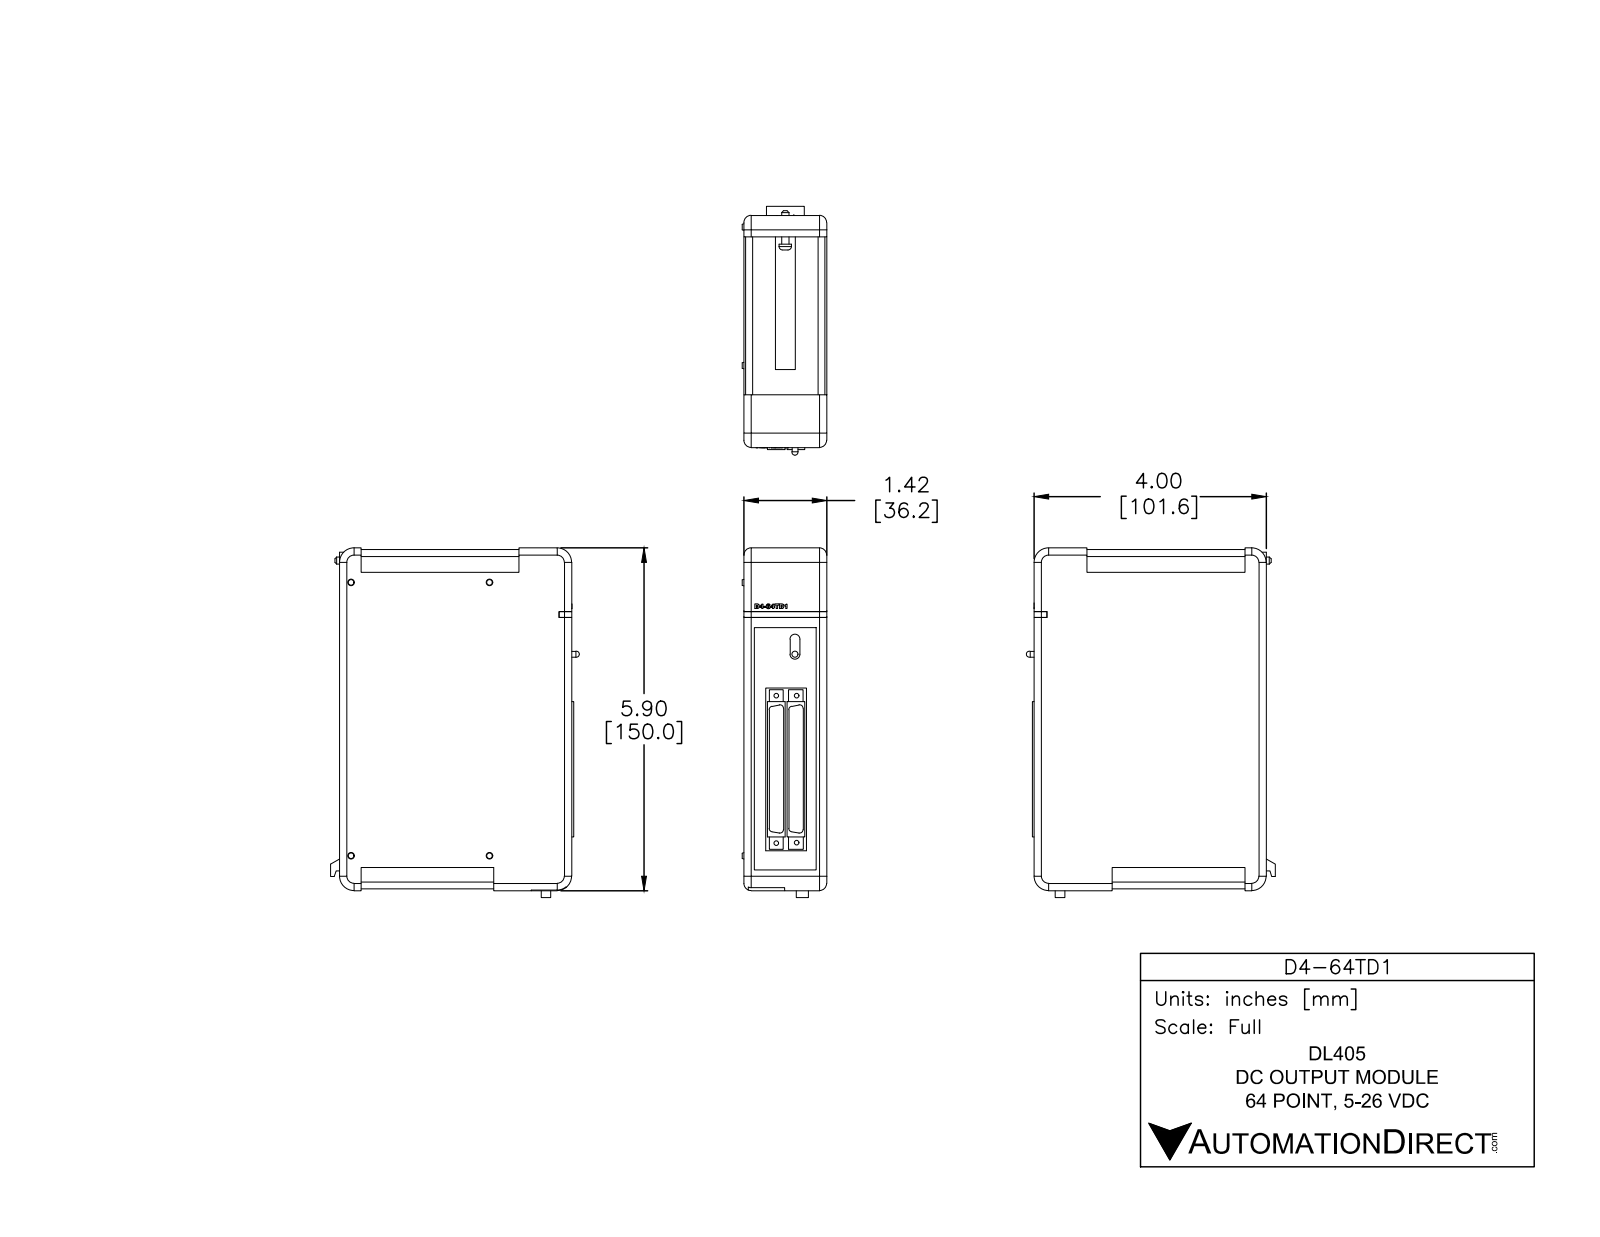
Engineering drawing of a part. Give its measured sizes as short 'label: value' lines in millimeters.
name: D4-64TD1
written by: SolidWorks 2014 (AUTOMOTIVE_DESIGN)
unit: mm
bodies: 2 solids, 313 faces (212 planar, 54 cylindrical, 47 other)
size: 153 × 108.8 × 37
volume: 524 200 mm³; area: 55 300 mm²
holes: 4× ⌀2
bosses: 1× ⌀5.4, 1× ⌀3.1, 1× ⌀2.5
rounds: 8× R1.5, 8× R3.2, 4× R3, 4× R6.4, 2× R2.2, 1× R3.7, 1× R4.3
face distances: 36.2, 0.8, 35.4, 100.8, 148.5, 149.2, 101.6, 5.1, 3.9, 95.8
hole spacings: 8.9, 64.3, 64.5, 64.9, 65.1
